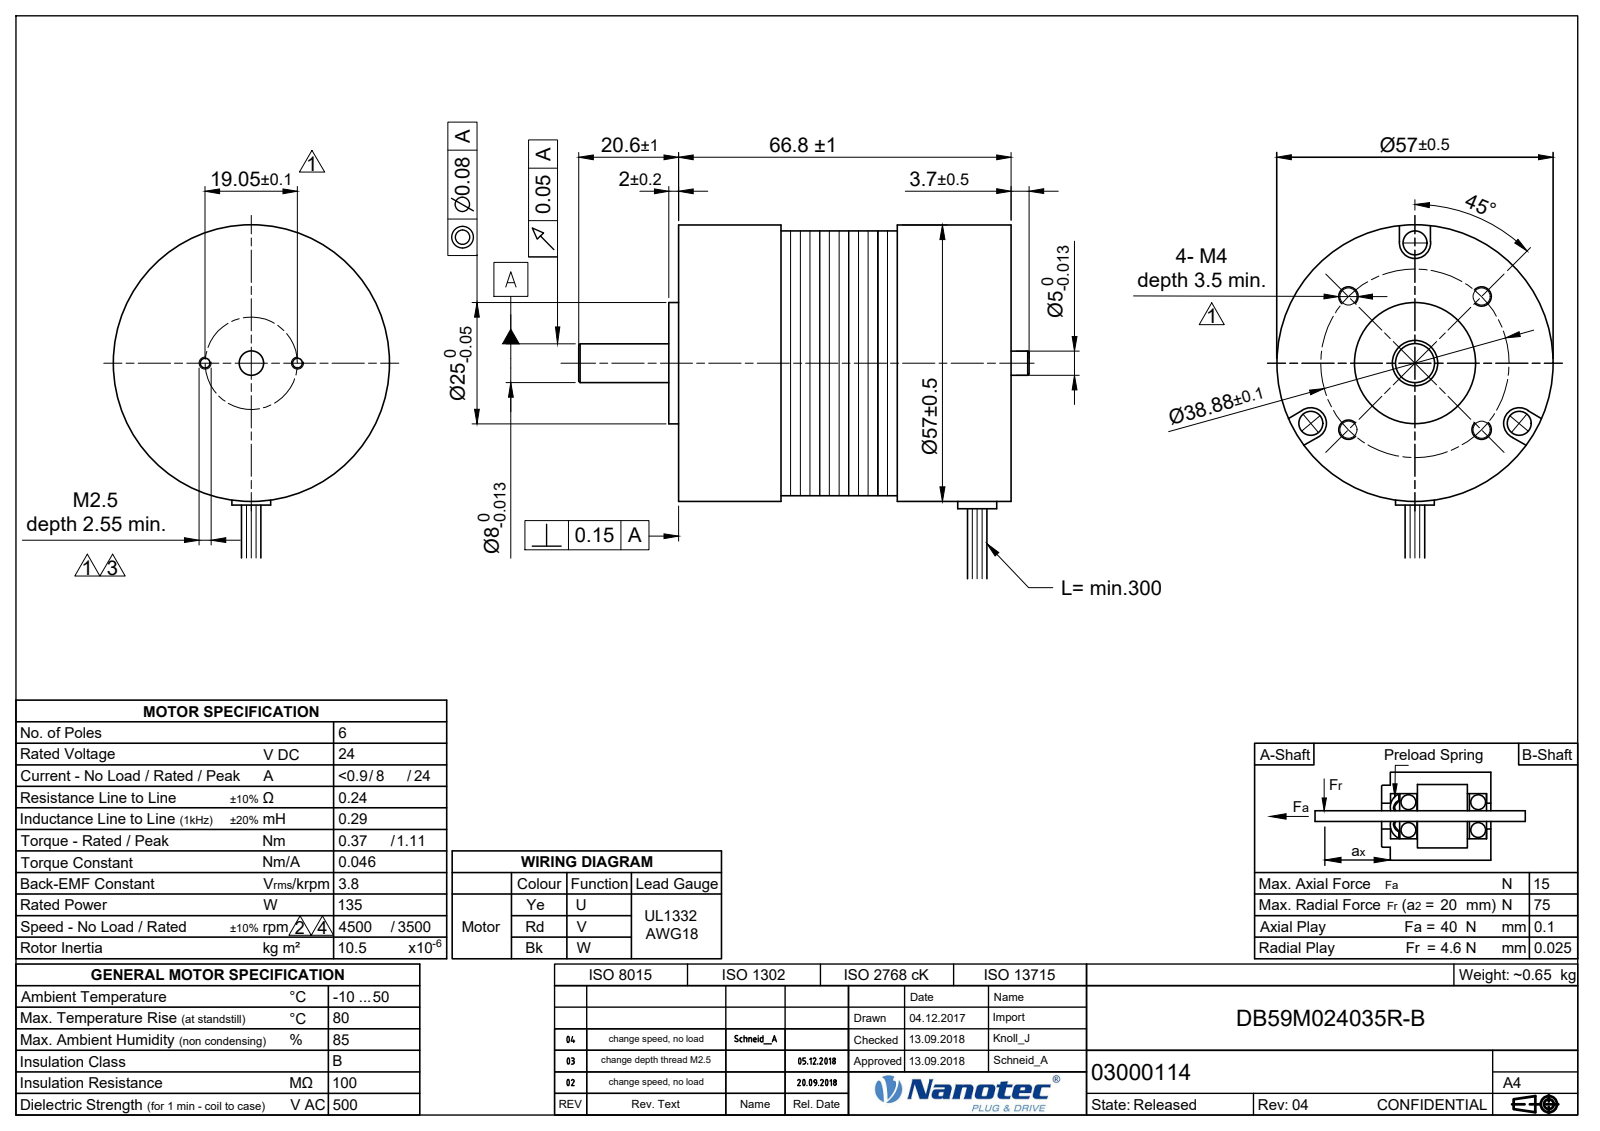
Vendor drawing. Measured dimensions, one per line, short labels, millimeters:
name: DB59M024035R-B
written by: Autodesk Inventor 2017 (AUTOMOTIVE_DESIGN)
unit: mm
bodies: 8 solids, 167 faces (80 planar, 30 cylindrical, 57 other)
size: 91.1 × 88.53 × 57
volume: 167 578 mm³; area: 32 724 mm²
holes: 4× ⌀3.24, 3× ⌀3.4, 2× ⌀2.01, 1× ⌀6.35, 1× ⌀8, 1× ⌀8.5, 1× ⌀13
bosses: 3× ⌀3, 3× ⌀2.75, 1× ⌀57, 1× ⌀55, 1× ⌀25, 1× ⌀11, 1× ⌀5.5, 1× ⌀5
rounds: 3× R3.25
face distances: 29.2, 23.1, 52.3, 66.8, 43.7, 14.5, 68.8, 45.7, 16.5, 2
hole spacings: 19.44, 27.49, 24.8, 9.52, 14.22, 14.55, 17.64, 26.94
